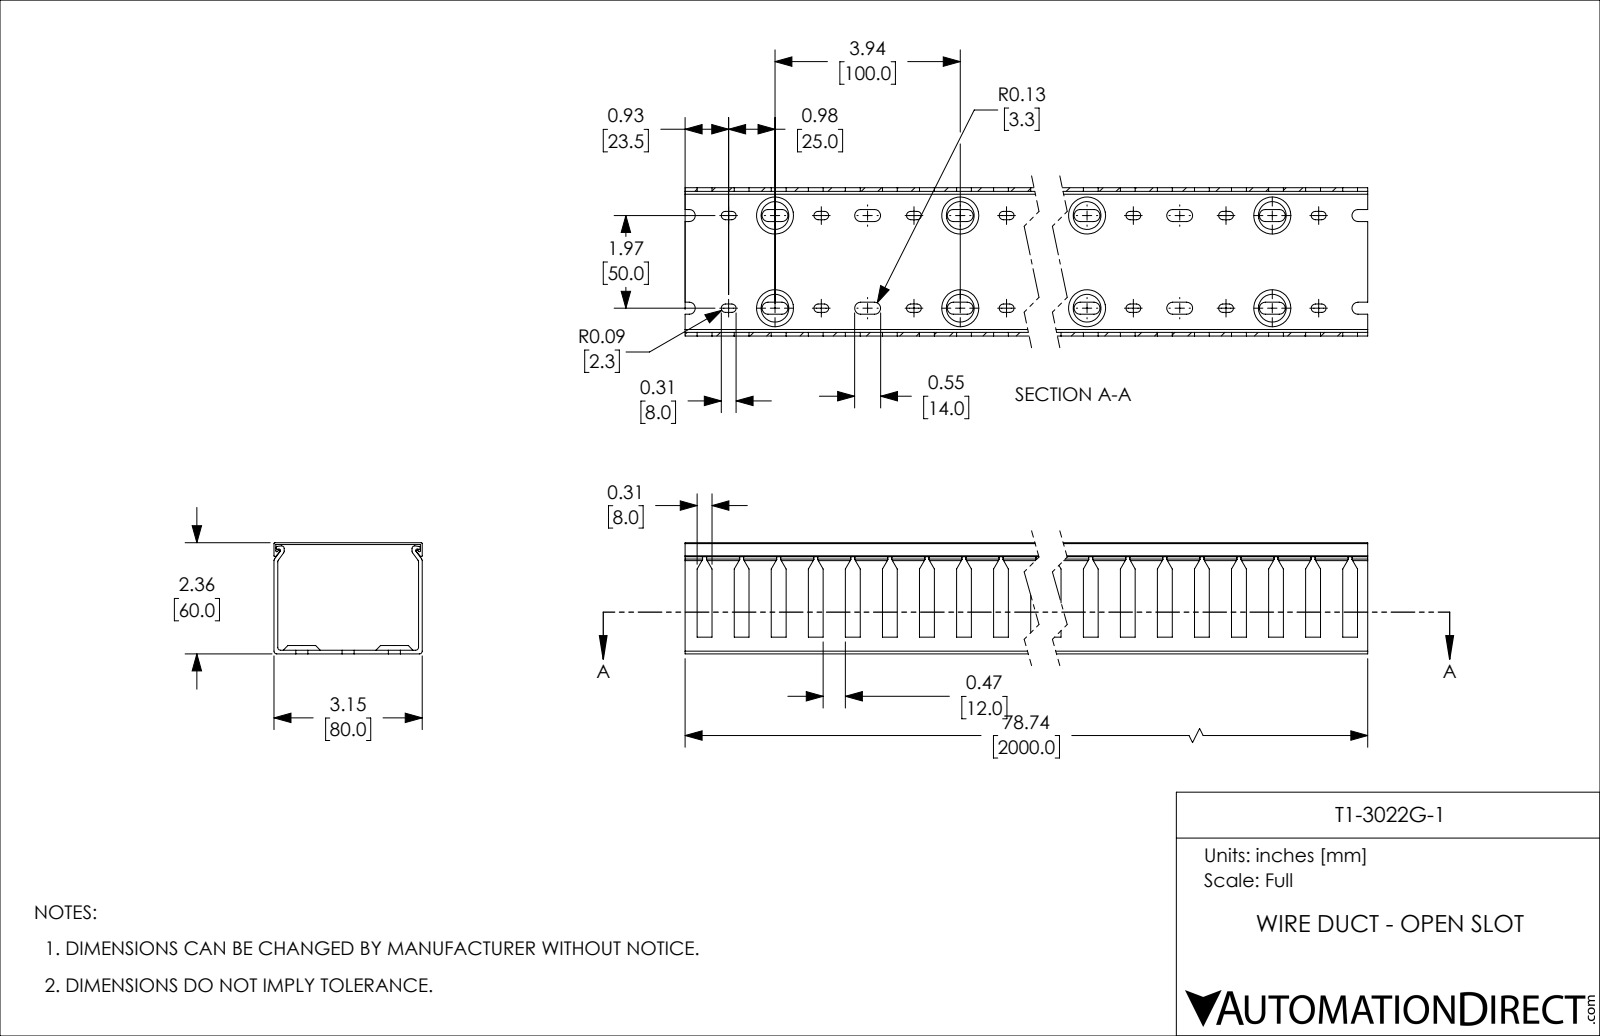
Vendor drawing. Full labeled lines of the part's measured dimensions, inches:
Part name (STEP PRODUCT): T1-3022G-1
STEP written by: SolidWorks 2021 (CONFIG_CONTROL_DESIGN)
Units: inches
Bodies: 2 solids, 1573 faces (762 planar, 731 cylindrical, 80 other)
Overall size (bounding box): 78.74 × 3.15 × 2.362
Volume: 59.21 in³ · Surface area: 1 810 in²
Partial cylindrical surfaces — rounded edges, fillets, slot ends (radius × count): R0.128 ×200, R0.089 ×160, R0.059 ×12, R0.02 ×8, R0.03 ×6
Main face-to-face distances: 0.079, 0.039, 3.071, 2.362, 2.323, 2.244, 2.283, 3.15, 2.992, 3.11
